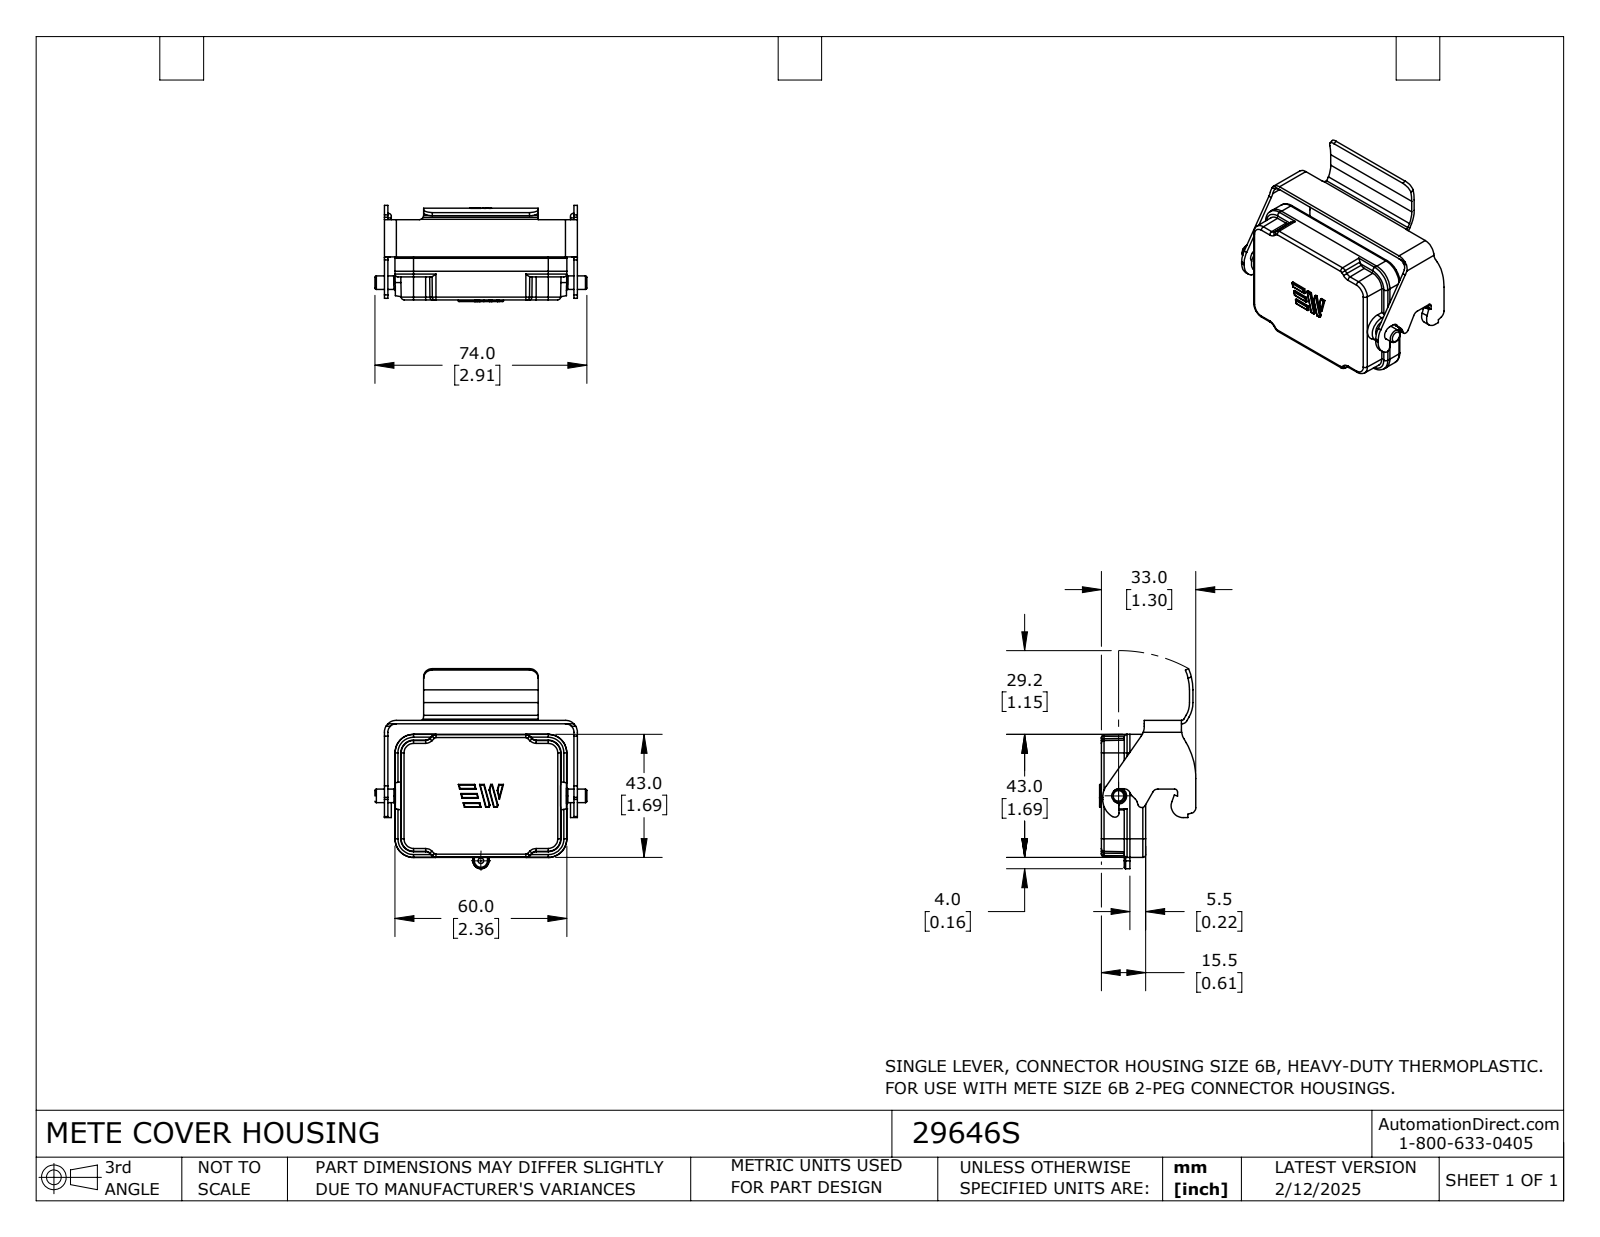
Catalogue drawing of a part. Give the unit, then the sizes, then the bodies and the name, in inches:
Units: inches
Overall size (bounding box): 2.913 × 2.75 × 1.323
Round bosses / shafts (diameter × count): ⌀0.185 ×1
Partial cylindrical surfaces — rounded edges, fillets, slot ends (radius × count): R0.008 ×33, R0.039 ×28, R0.02 ×13, R0.118 ×5, R0.11 ×4, R0.256 ×4, R0.079 ×3, R0.098 ×3
Main face-to-face distances: 0.047, 0.079, 0.146, 2.606, 2.559, 2.654, 0.102, 0.291, 0.067, 1.547
Volume: 0.955 in³ · Surface area: 26.12 in²
Bodies: 1 solid, 391 faces (148 planar, 160 cylindrical, 83 other)
Part name (STEP PRODUCT): 29646S
STEP written by: SolidWorks 2024 (CONFIG_CONTROL_DESIGN)
